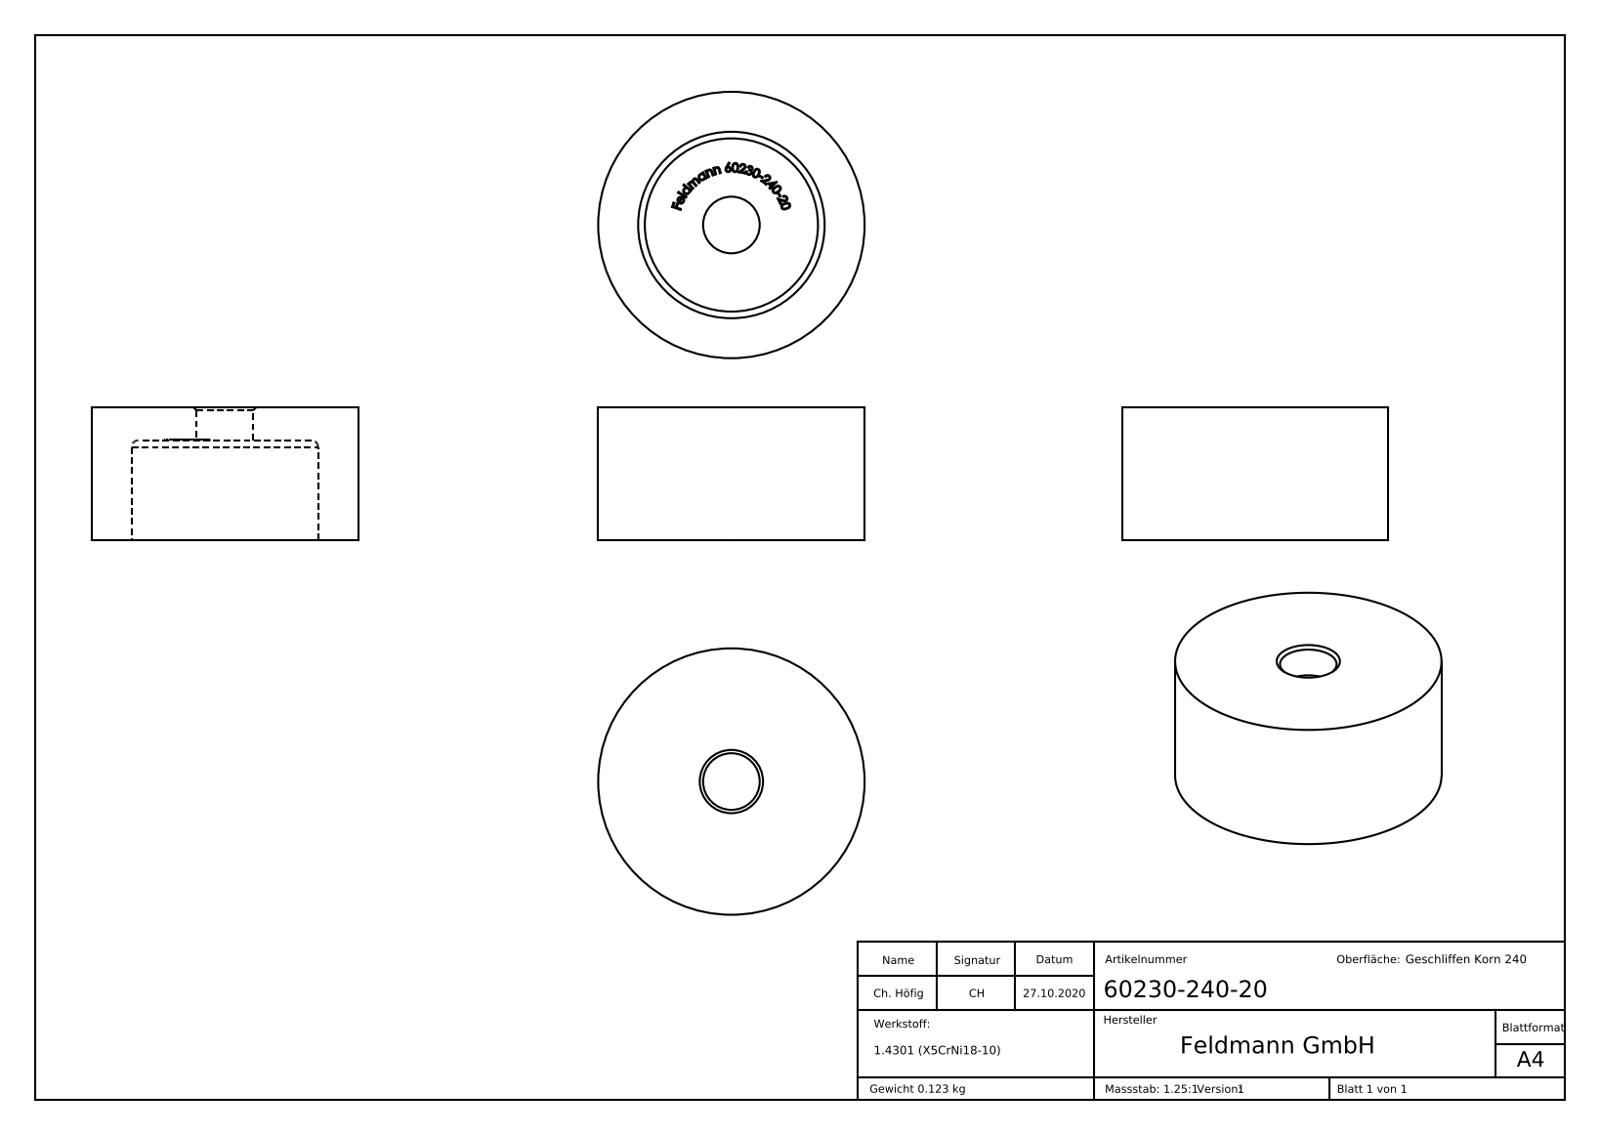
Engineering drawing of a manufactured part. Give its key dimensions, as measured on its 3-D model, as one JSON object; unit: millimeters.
{"part_name": "60230-240-20", "step_written_by": "SolidWorks 2018 (CONFIG_CONTROL_DESIGN)", "units": "millimeters", "bodies": {"solids": 1, "faces": 266, "planar": 131, "cylindrical": 6, "other": 129}, "overall_size": [40, 40, 20], "volume_mm3": 15627, "surface_area_mm2": 6332, "round_holes": [[8.5, 1], [28, 1]], "round_bosses_or_shafts": [[40, 1]], "face_to_face_distances": [20, 15, 5, 15.1, 4.9, 0.54, 0.66, 0.67, 0.72, 0.79]}
